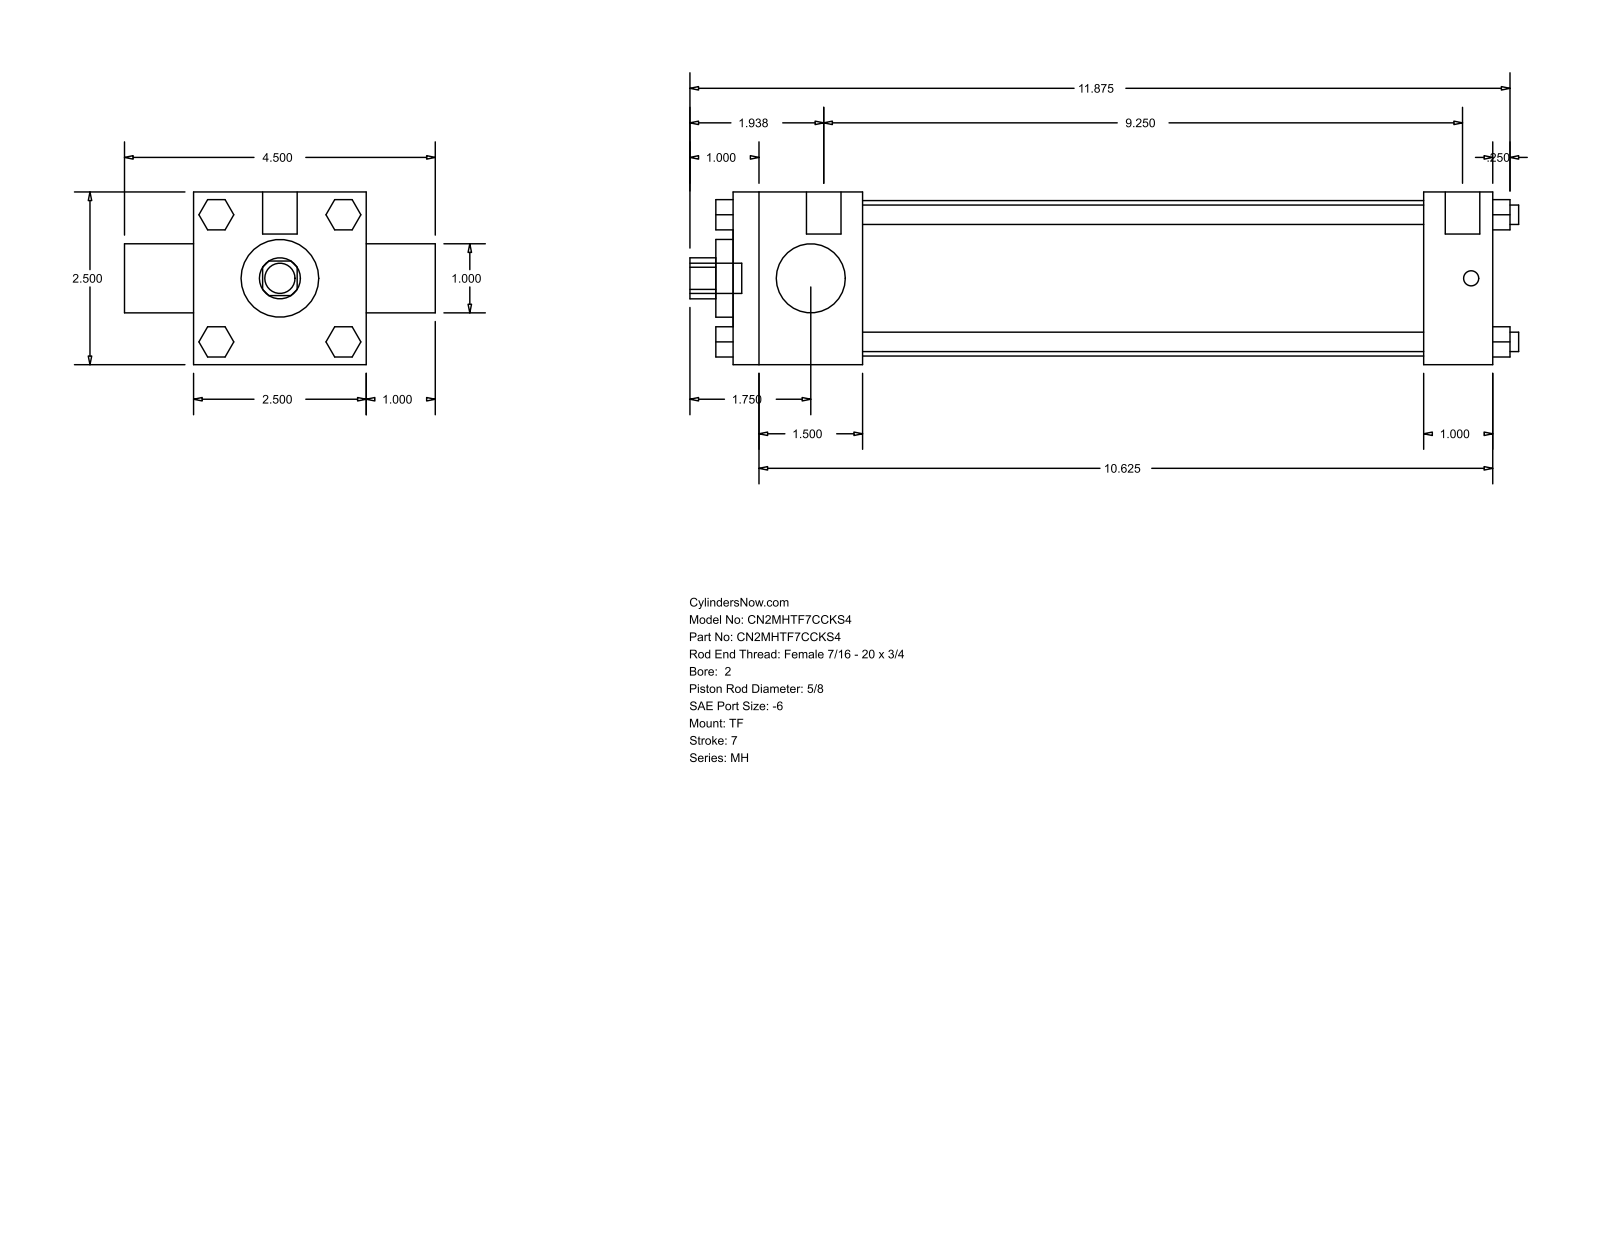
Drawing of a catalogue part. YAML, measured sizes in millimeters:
part_name: "MH_TF__0200_0.625"
step_written_by: "GSSL Pune (CONFIG_CONTROL_DESIGN)"
units: millimeters
bodies: {solids: 0, faces: 120, planar: 92, cylindrical: 28, other: 0}
overall_size: [304.8, 114.3, 63.5]
round_holes:
  - {diameter: 15.88, count: 1}
  - {diameter: 25.4, count: 1}
  - {diameter: 28.57, count: 1}
  - {diameter: 57.15, count: 1}
round_bosses_or_shafts:
  - {diameter: 7.14, count: 4}
  - {diameter: 5.56, count: 3}
  - {diameter: 12.7, count: 2}
  - {diameter: 11.11, count: 1}
partial_cylinders:
  - {radius: 7.54, count: 1}
face_to_face_distances: [63.5, 279.39, 47.62, 254, 206.38, 231.77, 25.39, 25.4, 6.35, 88.9]
